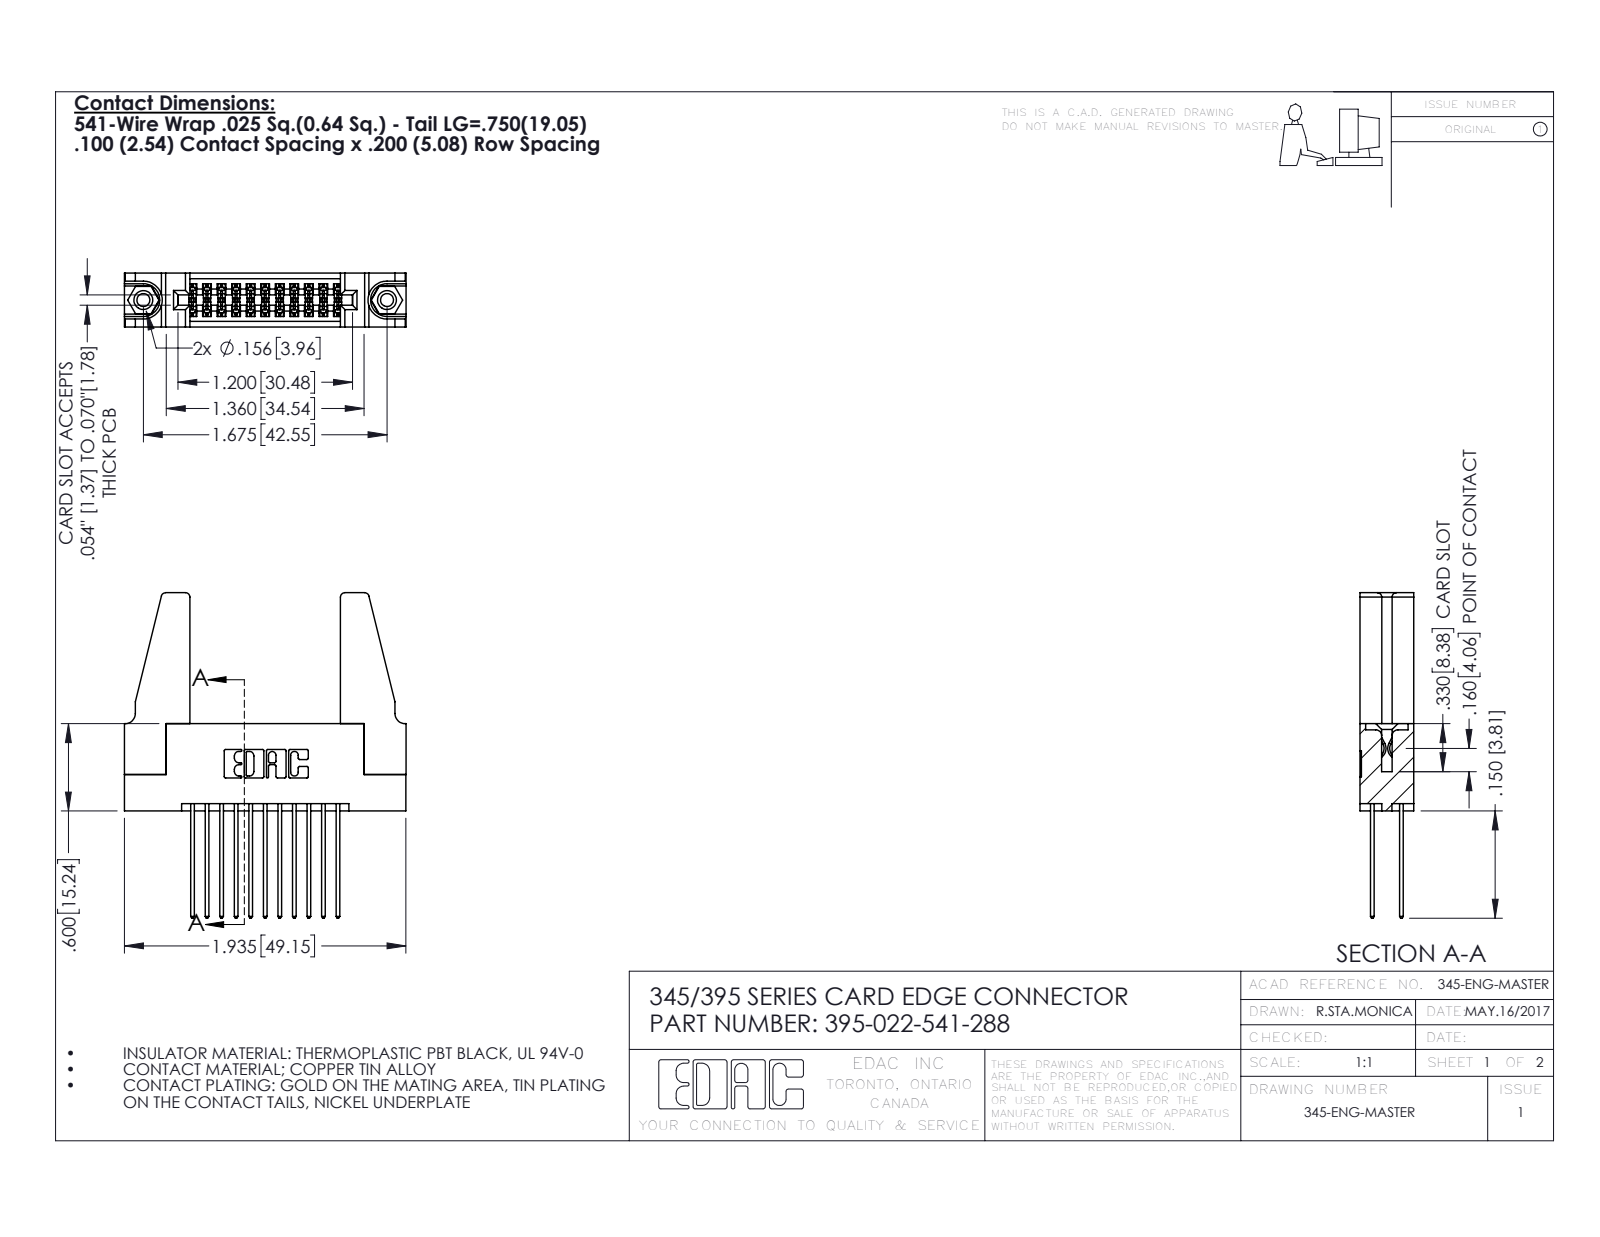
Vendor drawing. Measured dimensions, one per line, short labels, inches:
name: 345-292-001_345-293-141; 345-220-078_345-220-088; 345 Part_Flush Mounting Lugs - 0.156 Dia-TH; 395-022-541-288 (+1 more)
written by: SolidWorks 2016 (CONFIG_CONTROL_DESIGN)
unit: in
bodies: 27 solids, 1350 faces (878 planar, 456 cylindrical, 16 other)
size: 2.237 × 1.936 × 0.37
volume: 0.48 in³; area: 15.4 in²
holes: 2× ⌀0.089, 2× ⌀0.125, 2× ⌀0.156, 1× ⌀0.064
bosses: 2× ⌀0.155
rounds: 33× R0.006, 22× R0.01, 22× R0.01, 8× R0.03, 6× R0.007, 6× R0.031, 3× R0.026, 2× R0.014
face distances: 0.072, 0.37, 0.298, 0.2, 0.098, 0.272, 0.025, 0.225, 0.175, 0.148
hole spacings: 0.27, 1.443, 1.675
